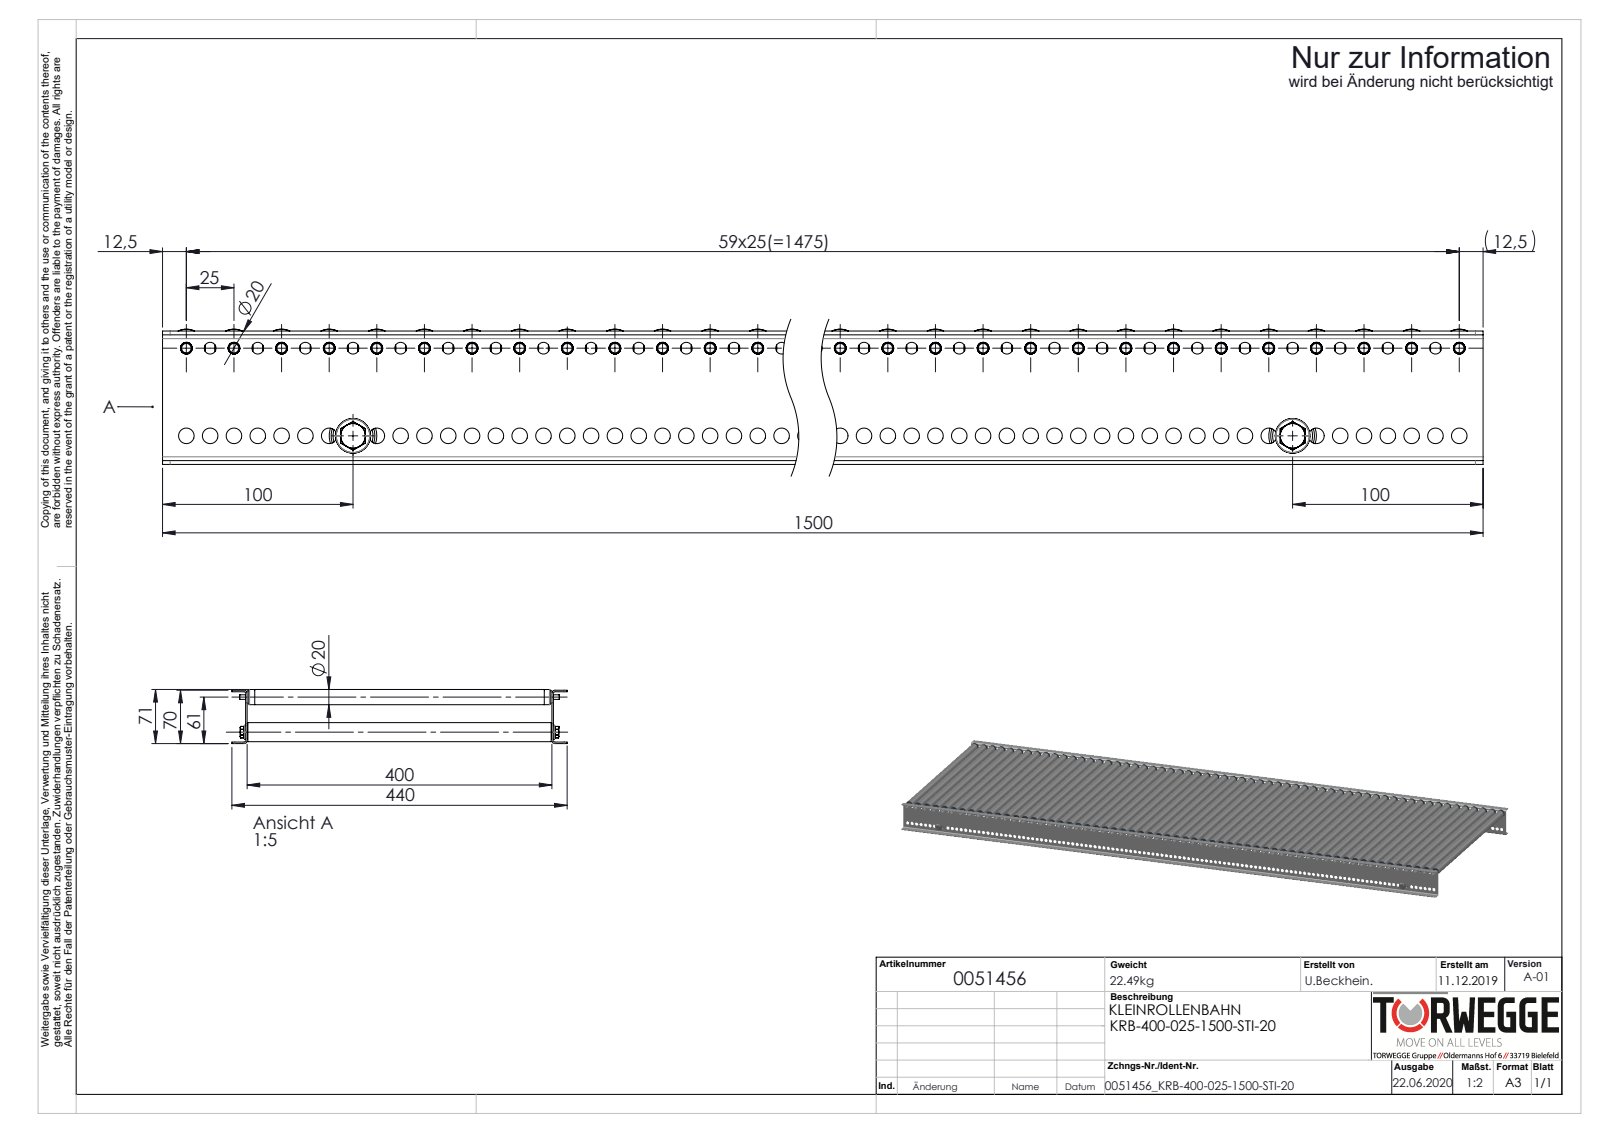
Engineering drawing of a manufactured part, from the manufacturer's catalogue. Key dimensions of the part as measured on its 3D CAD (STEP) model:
Part name (STEP PRODUCT): 0051456; Profil_KRB-20x70x20x2_KFG_S100205_U-PROFIL-20-70-20-2-KRB-20-L=1500; S100992_Typ-KUT50-20x1-6; S100994_Sperrzahnschraube_M08x16-8.8-A2K (+4 more)
STEP written by: SolidWorks 2020 (AUTOMOTIVE_DESIGN)
Units: millimetres
Bodies: 132 solids, 11792 faces (3840 planar, 4488 cylindrical, 3464 other)
Overall size (bounding box): 1500 × 440 × 71
Volume: 2 798 000 mm³ · Surface area: 4 334 000 mm²
Round holes (diameter × count): ⌀6.2 ×119, ⌀8.2 ×119, ⌀6.1 ×60, ⌀14.2 ×60, ⌀17.2 ×60, ⌀18 ×60, ⌀6.8 ×2, ⌀21 ×2
Round bosses / shafts (diameter × count): ⌀20 ×60, ⌀19.9 ×60, ⌀18.1 ×60, ⌀17.8 ×60, ⌀16.5 ×60, ⌀6 ×60, ⌀25 ×2, ⌀8 ×2
Partial cylindrical surfaces — rounded edges, fillets, slot ends (radius × count): R4.05 ×60, R4 ×8, R2 ×4
Main face-to-face distances: 2, 402, 68, 400, 404, 70, 66, 392, 18, 30
Hole centre spacings: 12.5, 25, 37.5, 50, 62.5, 75, 87.5, 100
